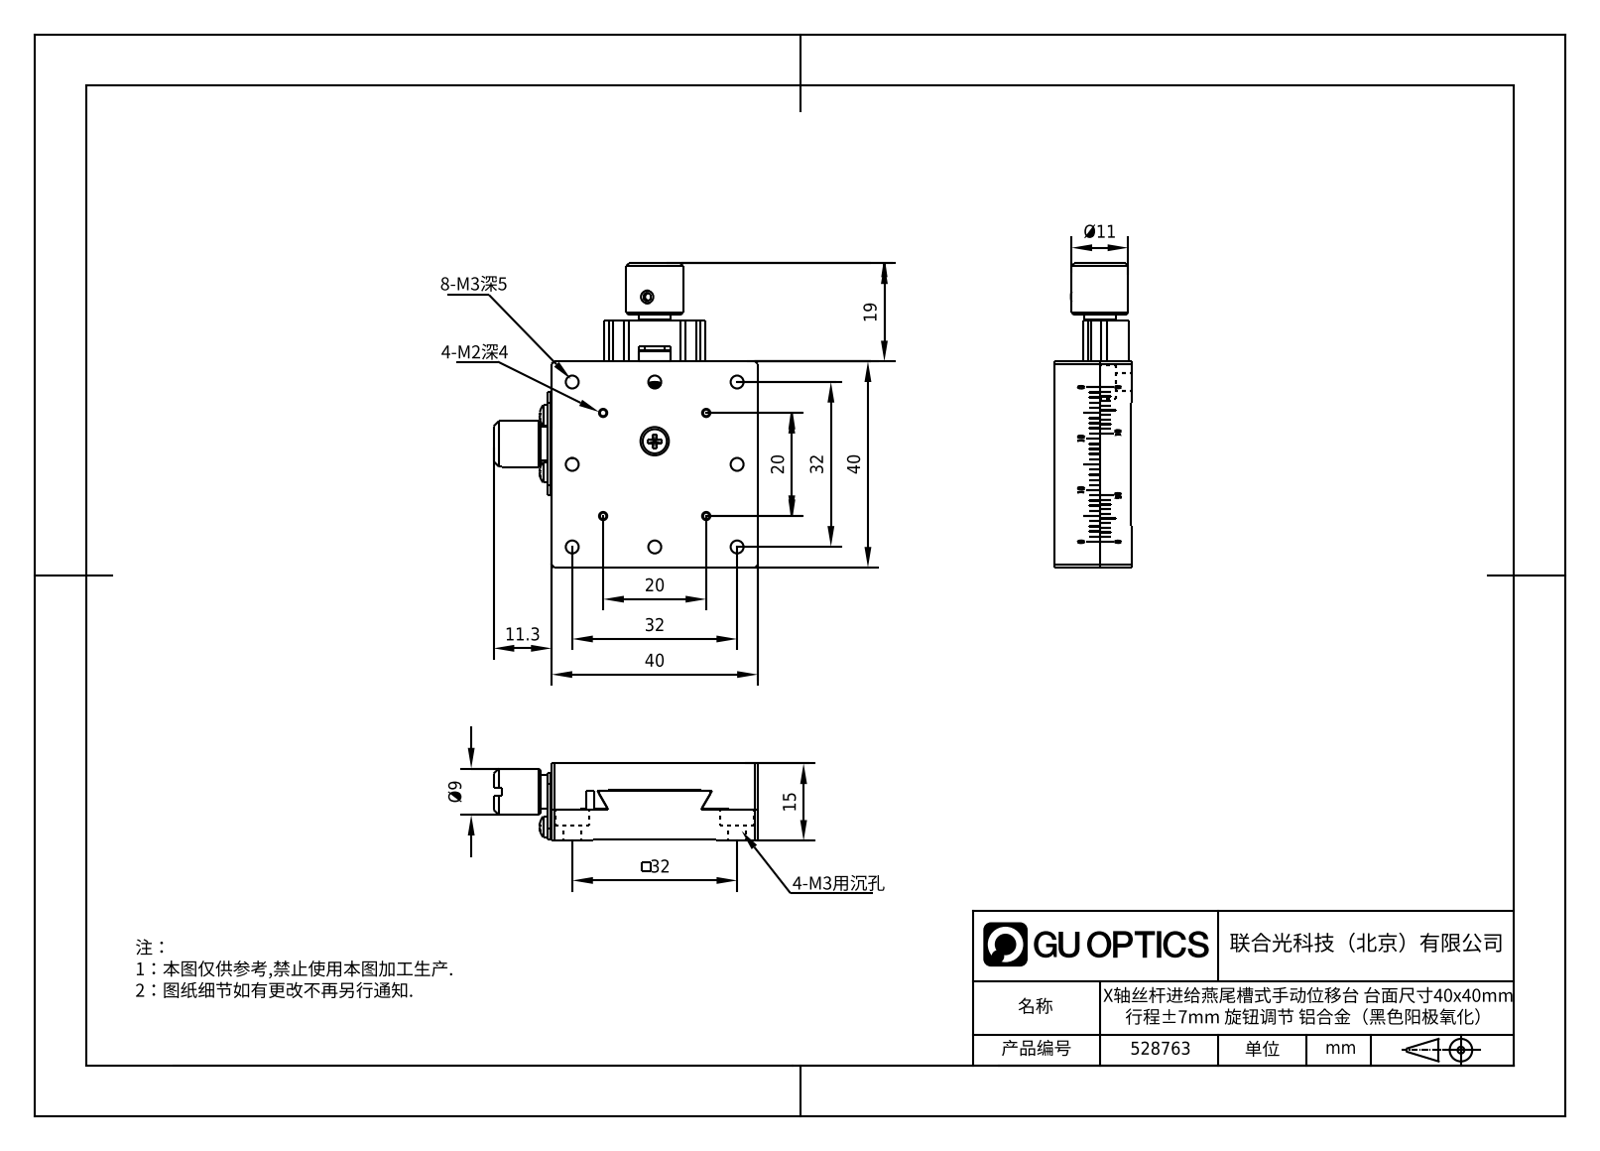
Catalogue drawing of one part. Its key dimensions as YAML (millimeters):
part_name: "528763"
step_written_by: "SolidWorks 2020 (CONFIG_CONTROL_DESIGN)"
units: millimeters
bodies: {solids: 15, faces: 690, planar: 465, cylindrical: 88, other: 137}
overall_size: [59, 51.25, 15]
volume: 23620
surface_area: 15628
round_holes:
  - {diameter: 2.5, count: 14}
  - {diameter: 1.6, count: 6}
  - {diameter: 3.4, count: 4}
  - {diameter: 6.5, count: 4}
  - {diameter: 2.05, count: 3}
  - {diameter: 2.4, count: 2}
  - {diameter: 2.7, count: 2}
  - {diameter: 4, count: 2}
  - {diameter: 4.6, count: 2}
  - {diameter: 2.9, count: 1}
  - {diameter: 4.1, count: 1}
  - {diameter: 4.3, count: 1}
round_bosses_or_shafts:
  - {diameter: 2, count: 4}
  - {diameter: 6, count: 2}
  - {diameter: 4, count: 2}
  - {diameter: 3.8, count: 2}
  - {diameter: 3, count: 2}
  - {diameter: 11, count: 1}
  - {diameter: 9, count: 1}
  - {diameter: 6.9, count: 1}
partial_cylinders:
  - {radius: 0.3, count: 8}
  - {radius: 2, count: 6}
  - {radius: 1.6, count: 2}
  - {radius: 3.9, count: 2}
  - {radius: 3.1, count: 1}
face_to_face_distances: [9, 5.8, 14.8, 40, 3.6, 9.6, 9.4, 5.4, 3.8, 6]
hole_center_spacings: [11.66, 16, 26.68, 27.86, 35.78, 32, 8.49, 20]
